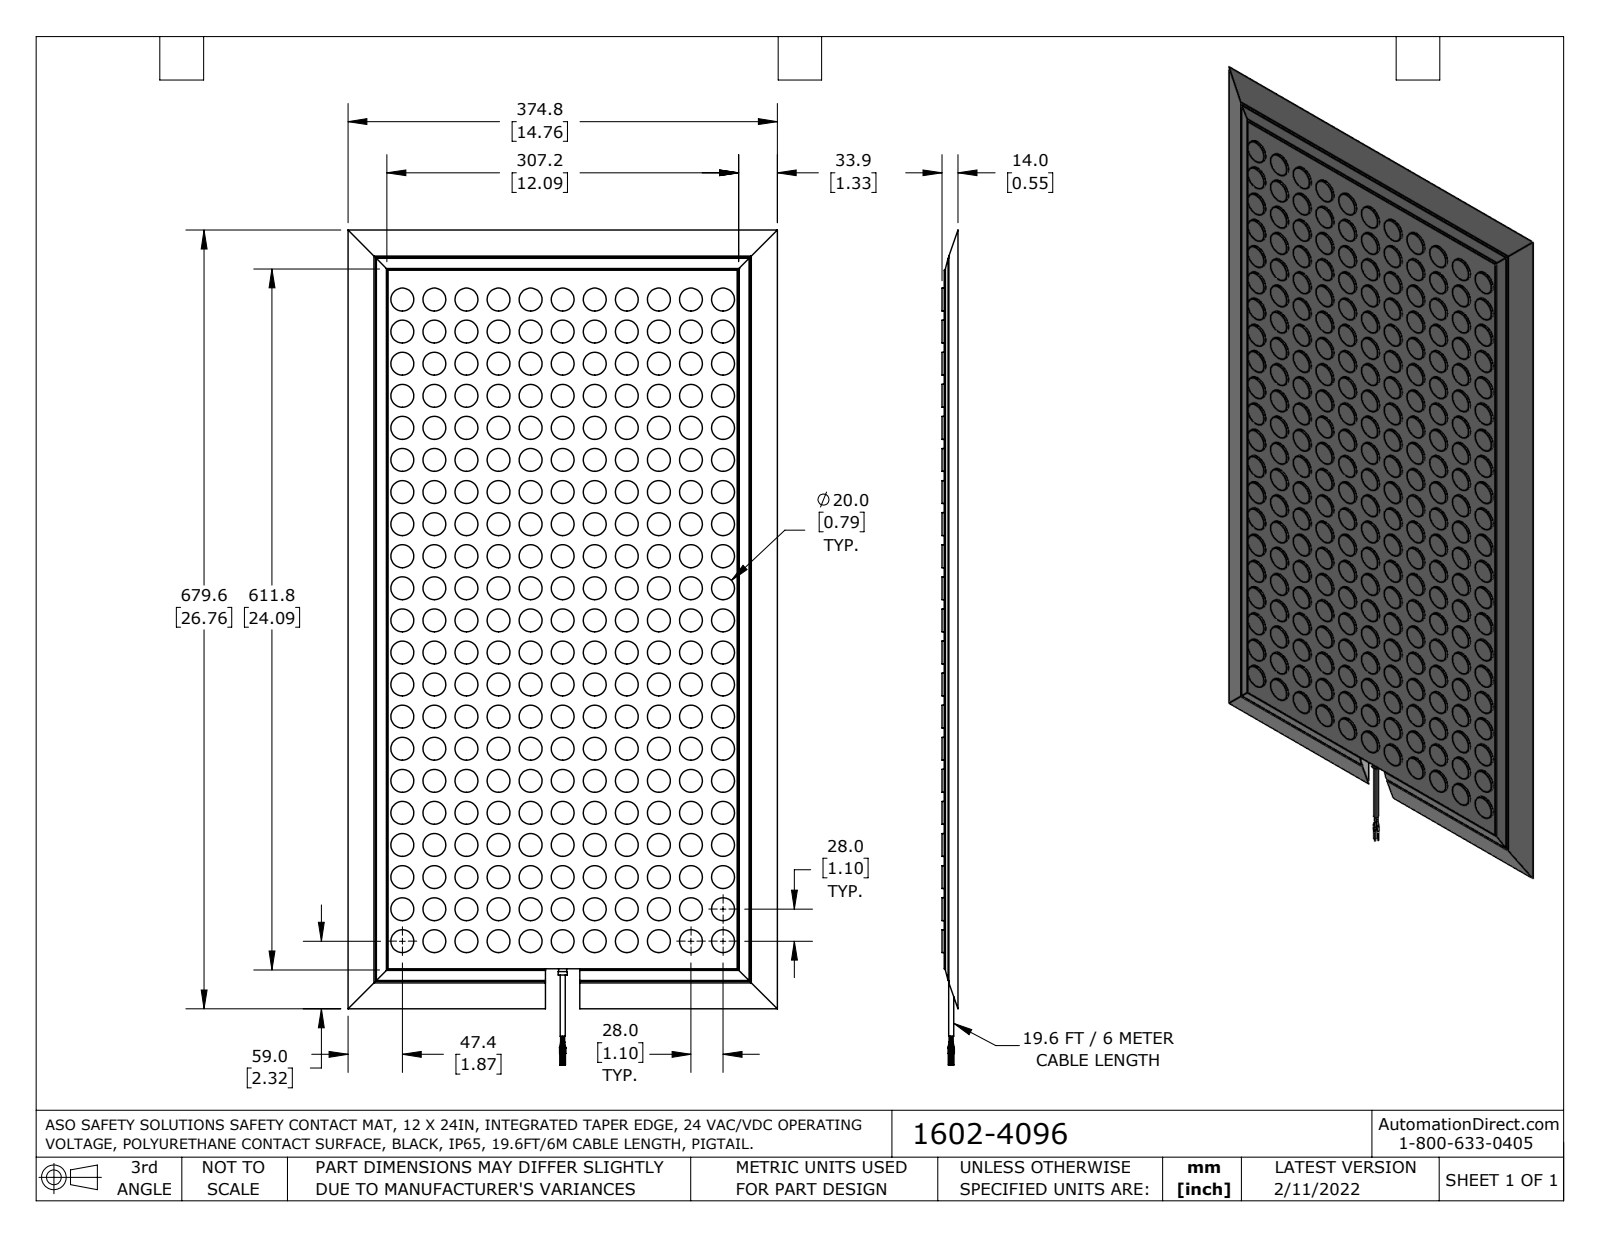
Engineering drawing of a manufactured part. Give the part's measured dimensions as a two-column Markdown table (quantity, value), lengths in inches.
| quantity | value |
| --- | --- |
| part name | 1602-4096_Default |
| STEP written by | SolidWorks 2021 (CONFIG_CONTROL_DESIGN) |
| units | inches |
| bodies | 3 solids, 866 faces (289 planar, 545 cylindrical, 32 other) |
| overall size | 28.685 × 14.756 × 0.551 |
| volume | 168.4 in³ |
| surface area | 874.3 in² |
| round holes (diameter × count) | 0.173 × 1 |
| round bosses / shafts (diameter × count) | 0.787 × 231, 0.047 × 20, 0.031 × 8, 0.315 × 1, 0.276 × 1 |
| partial cylindrical surfaces (radius × count) | 0.008 × 4 |
| main face-to-face distances | 0.472, 0.551, 0.079, 0.236, 12, 0.315, 24, 5.409, 6.591, 1.181 |
